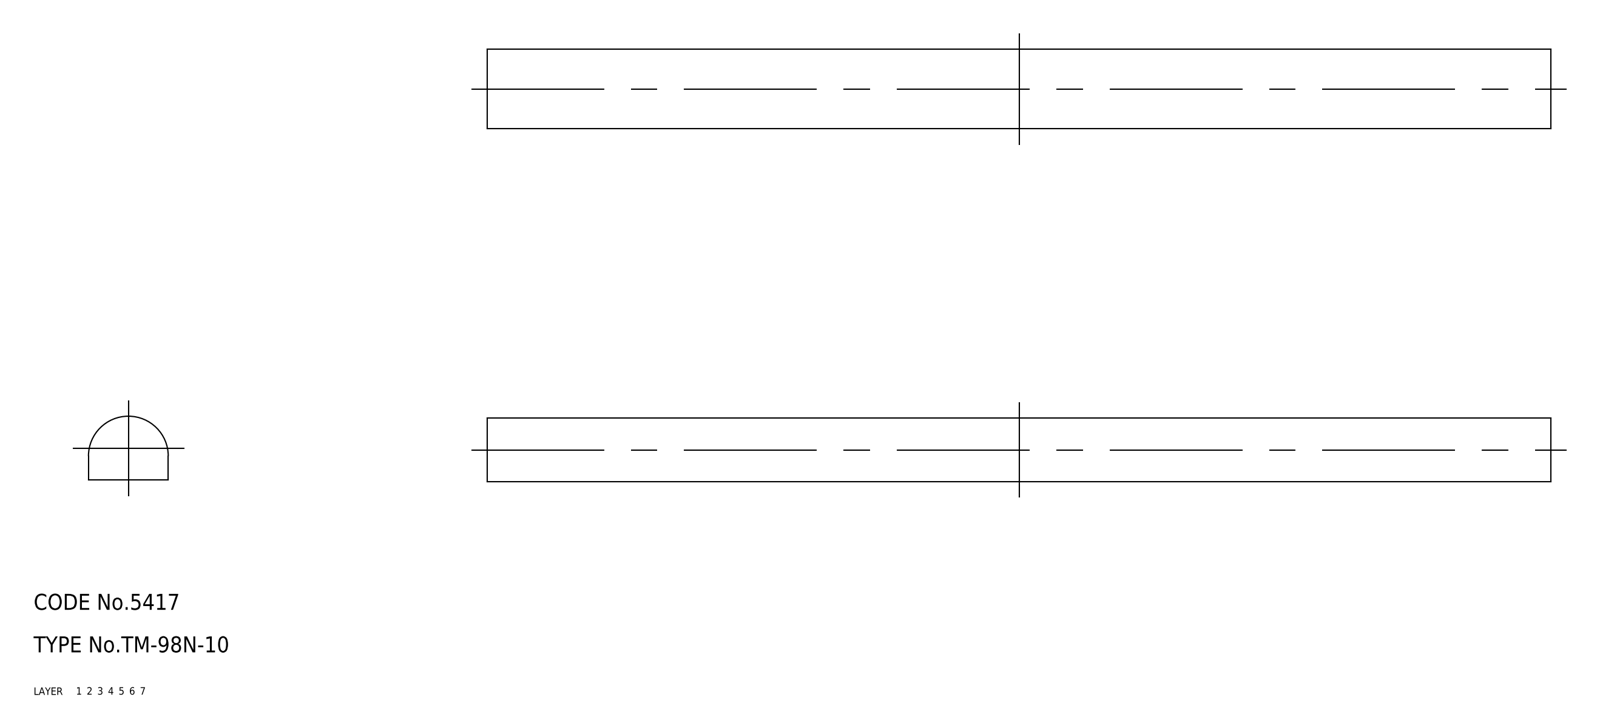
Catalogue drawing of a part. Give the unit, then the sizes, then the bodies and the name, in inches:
Units: inches
Overall size (bounding box): 7.874 × 0.591 × 0.472
Volume: 1.902 in³ · Surface area: 15.23 in²
Bodies: 1 solid, 6 faces (0 planar, 0 cylindrical, 6 other)
Part name (STEP PRODUCT): rubber foam
STEP written by: CADfix (AUTOMOTIVE_DESIGN)
